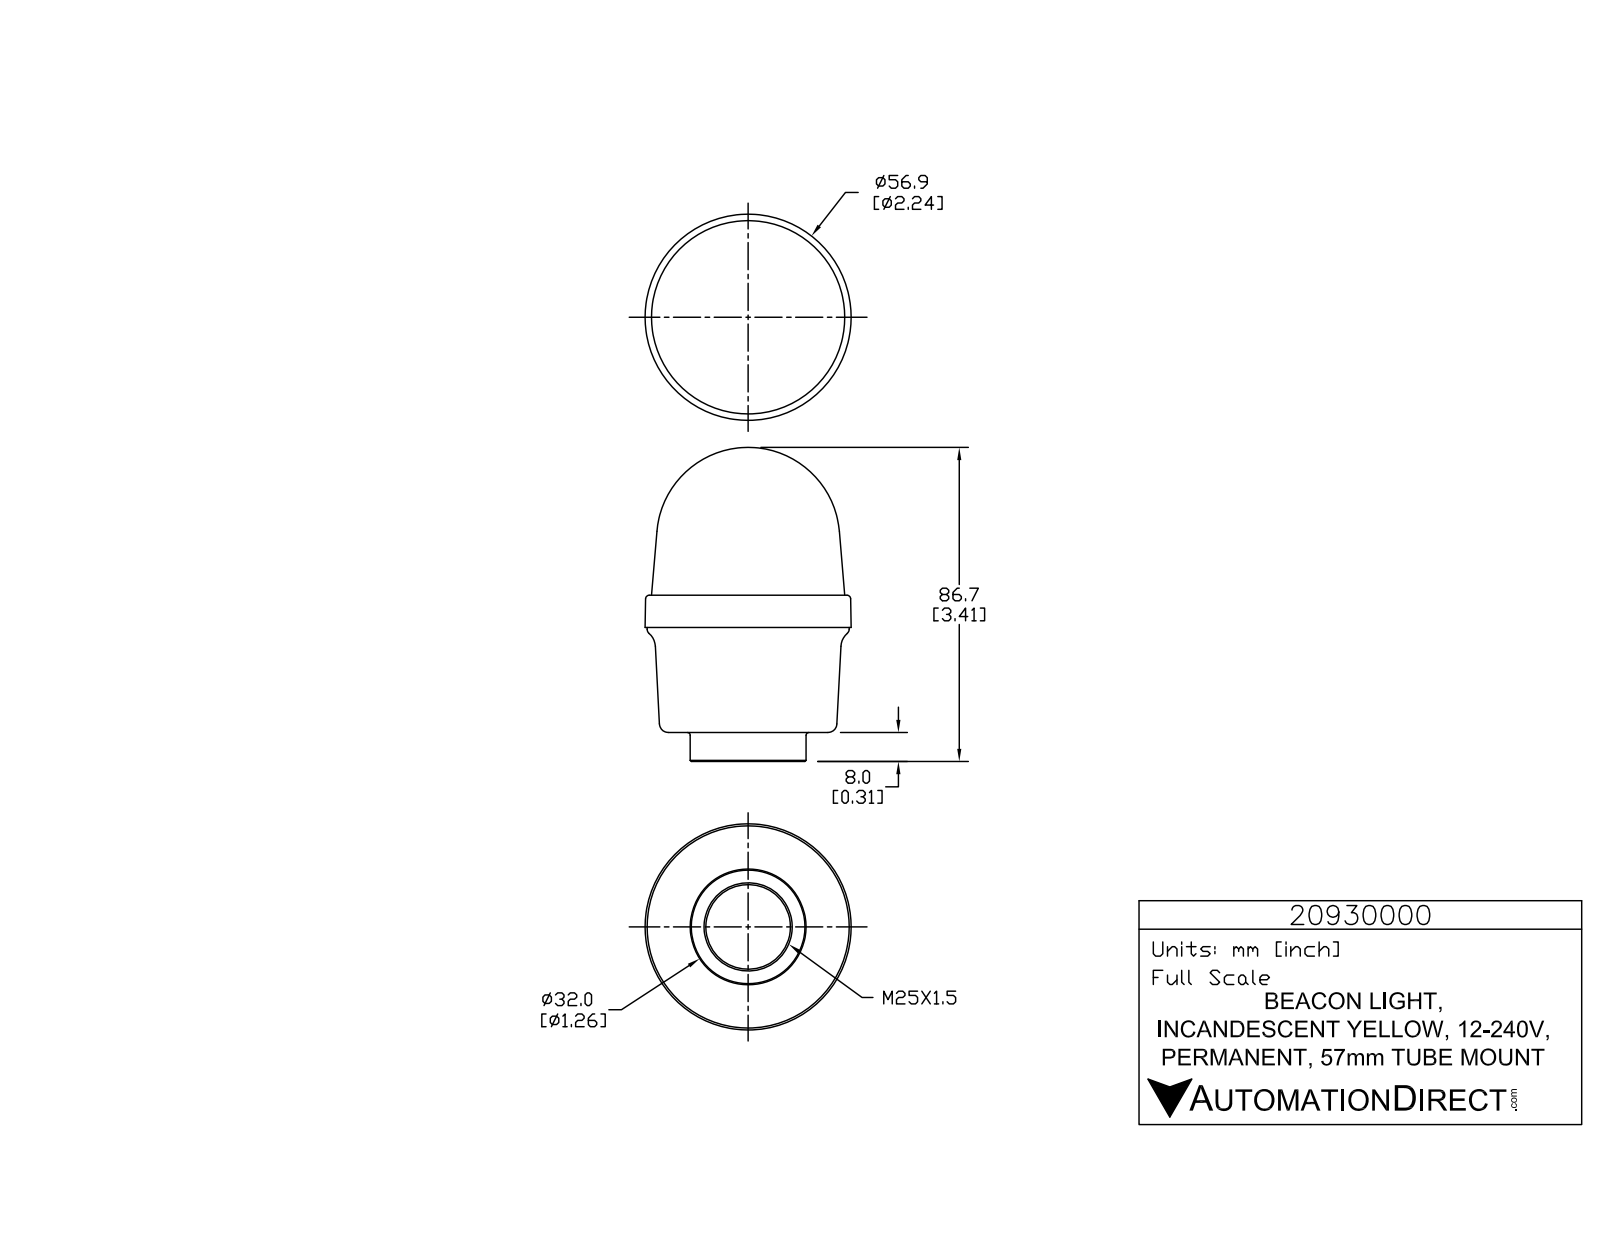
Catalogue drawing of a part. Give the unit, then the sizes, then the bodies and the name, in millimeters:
Units: millimetres
Overall size (bounding box): 86.7 × 56.9 × 56.9
Round holes (diameter × count): ⌀1 ×3, ⌀23.4 ×1
Round bosses / shafts (diameter × count): ⌀5.7 ×3, ⌀1.4 ×3, ⌀55.8 ×1, ⌀32 ×1
Partial cylindrical surfaces — rounded edges, fillets, slot ends (radius × count): R0.2 ×6, R0.2 ×6, R0.2 ×6, R3.3 ×6, R0.1 ×3, R0.1 ×3, R0.2 ×3, R0.2 ×3
Main face-to-face distances: 8, 37.9, 45.9, 8.9, 29, 37, 17.7, 8.8, 46.7, 54.7
Volume: 150 600 mm³ · Surface area: 16 310 mm²
Bodies: 1 solid, 787 faces (524 planar, 168 cylindrical, 95 other)
Part name (STEP PRODUCT): 20930000
STEP written by: SolidWorks 2015 (AUTOMOTIVE_DESIGN)
